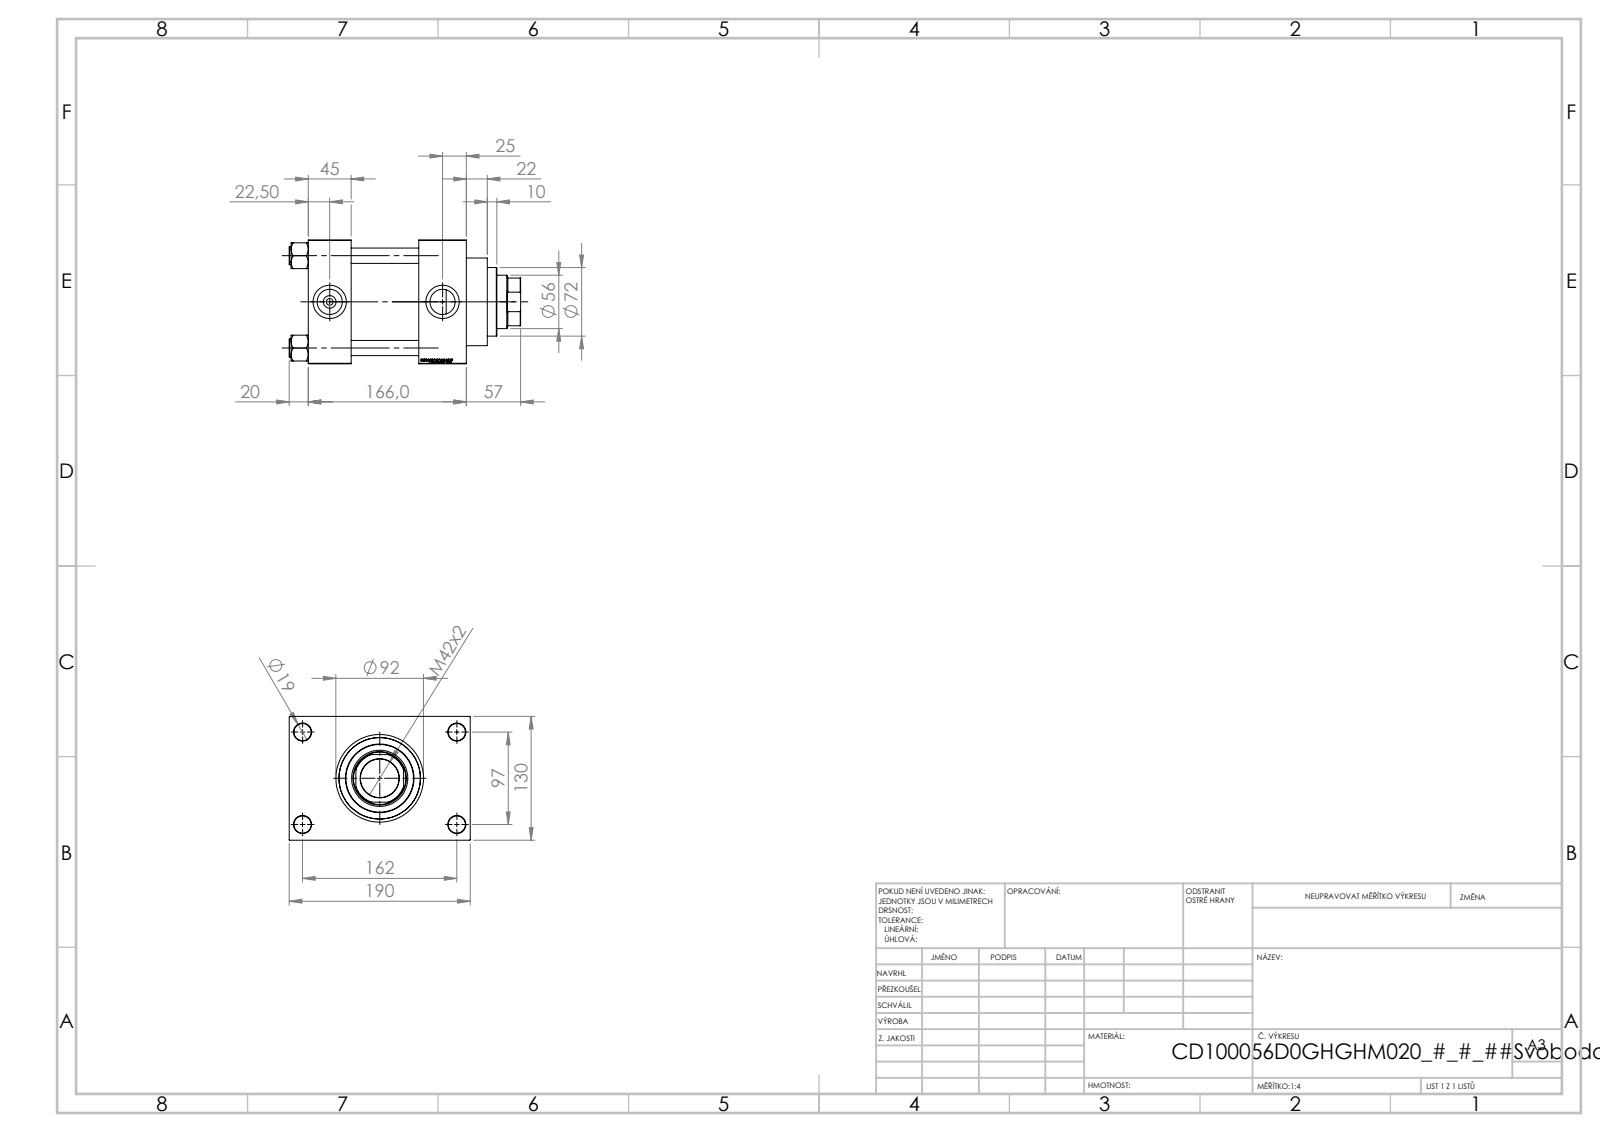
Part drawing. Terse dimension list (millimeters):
name: V215CD_NUT_M5_D; V215CD_D_Body; V215CD_VC_A; V215CD_D_TYCINKA (+1 more)
written by: SolidWorks 2019 (CONFIG_CONTROL_DESIGN)
unit: mm
bodies: 11 solids, 1151 faces (545 planar, 88 cylindrical, 518 other)
size: 243 × 190 × 130
volume: 2 628 000 mm³; area: 362 363 mm²
holes: 4× ⌀16, 4× ⌀18, 2× ⌀7, 2× ⌀26.44, 2× ⌀35, 1× ⌀40.5, 1× ⌀56, 1× ⌀59, 1× ⌀76, 1× ⌀85.5, 1× ⌀100
bosses: 4× ⌀19, 1× ⌀106, 1× ⌀92, 1× ⌀72
rounds: 1× R27
face distances: 130, 116, 50, 45, 71, 166, 121, 30, 160, 20
hole spacings: 32.55, 68.52, 94.41, 96.9, 102.27, 129.45, 161.73, 97
